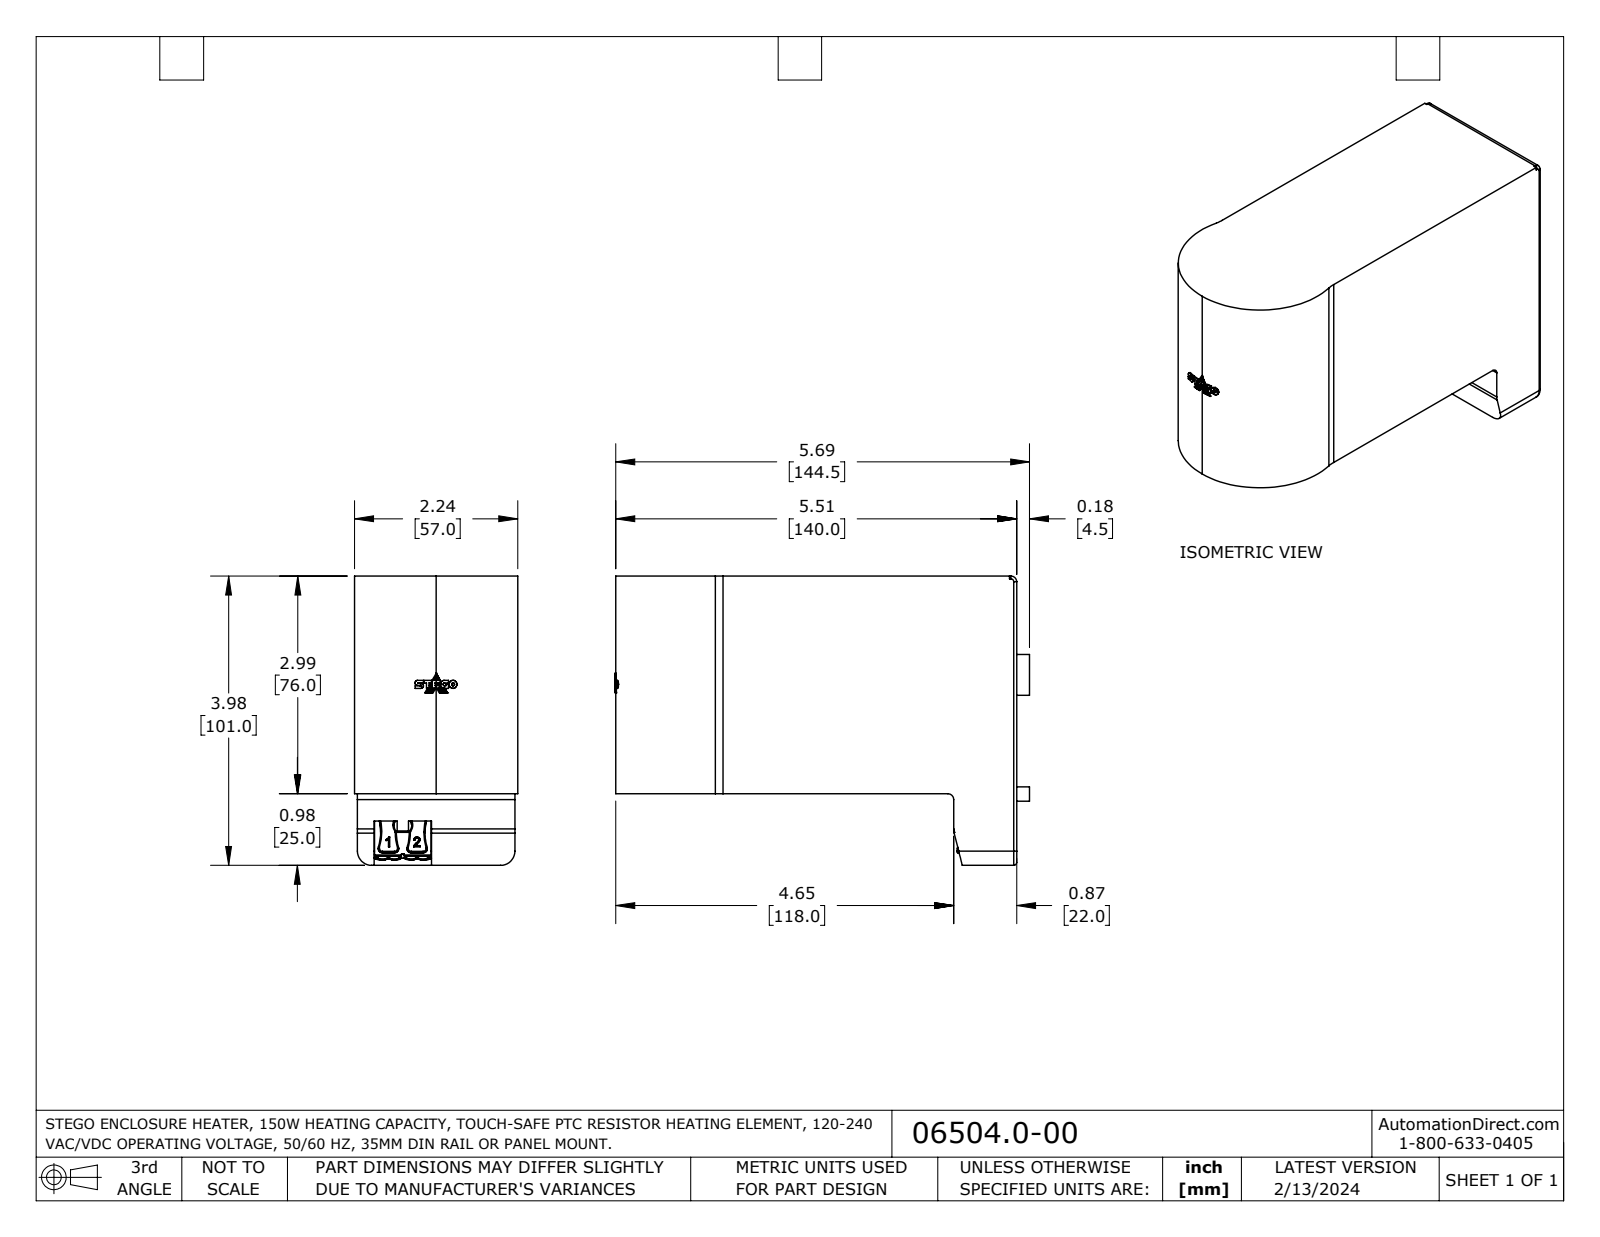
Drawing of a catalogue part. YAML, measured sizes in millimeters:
part_name: "STEP_LP065_1"
step_written_by: "SolidWorks 2022 (AUTOMOTIVE_DESIGN)"
units: millimeters
bodies: {solids: 1, faces: 467, planar: 228, cylindrical: 125, other: 114}
overall_size: [144.9, 101, 57]
volume: 125707
surface_area: 88422
partial_cylinders:
  - {radius: 0.4, count: 11}
  - {radius: 0.3, count: 6}
  - {radius: 2, count: 6}
  - {radius: 1, count: 5}
  - {radius: 0.7, count: 4}
  - {radius: 1.5, count: 4}
  - {radius: 18.75, count: 4}
  - {radius: 2.5, count: 2}
face_to_face_distances: [2.5, 52.5, 73.5, 55, 50, 76, 71, 5, 25, 98.5]
